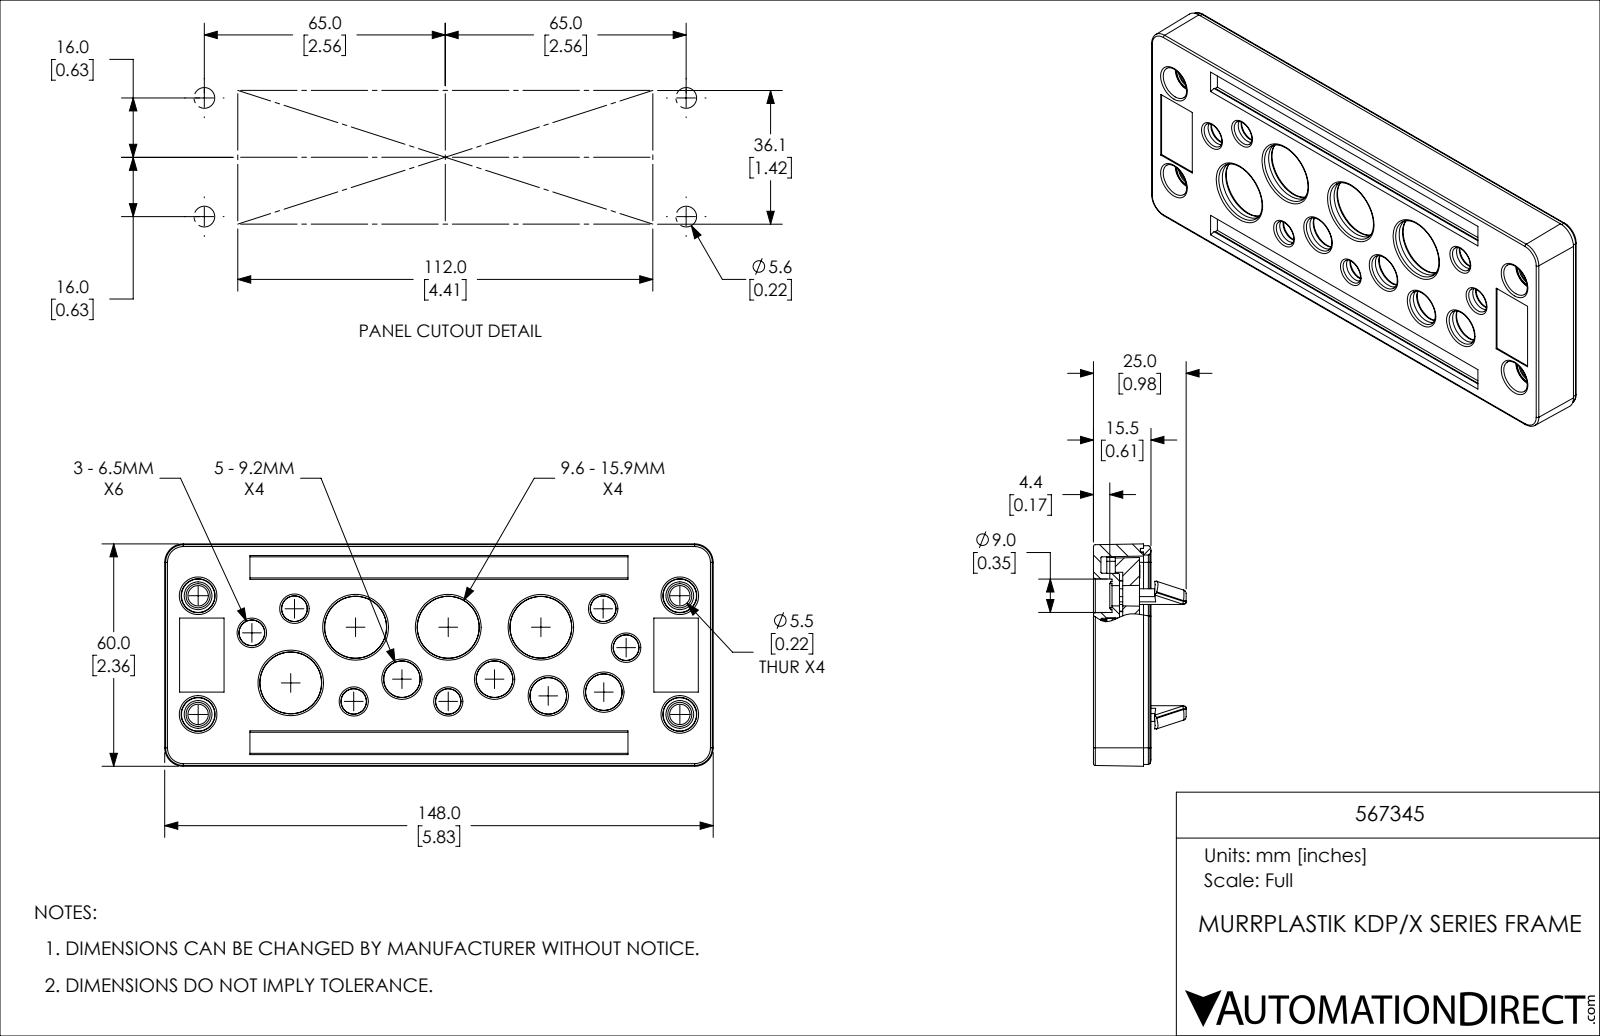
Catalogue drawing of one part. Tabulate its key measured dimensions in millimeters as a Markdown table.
| quantity | value |
| --- | --- |
| part name | 567345 |
| STEP written by | SolidWorks 2019 (CONFIG_CONTROL_DESIGN) |
| units | millimeters |
| bodies | 4 solids, 2816 faces (925 planar, 766 cylindrical, 1125 other) |
| overall size | 148 × 60 × 25 |
| volume | 72 226 mm³ |
| surface area | 69 875 mm² |
| round holes (diameter × count) | 3.6 × 10, 5.5 × 4, 6.5 × 4, 5 × 2, 2.6 × 1, 3.1 × 1 |
| round bosses / shafts (diameter × count) | 7.5 × 4, 3 × 1, 2.5 × 1 |
| partial cylindrical surfaces (radius × count) | 0.2 × 73, 0.3 × 43, 0.45 × 30, 1 × 28, 0.5 × 12, 2 × 12, 0.8 × 8, 2.75 × 4 |
| main face-to-face distances | 2.3, 5.9, 3.3, 3.6, 2, 6.5, 8.8, 12.4, 3.9, 1.6 |
| hole center spacings | 10.09, 22.04, 23.13, 26.59, 35.31, 42.8, 44.44, 62.1 |
